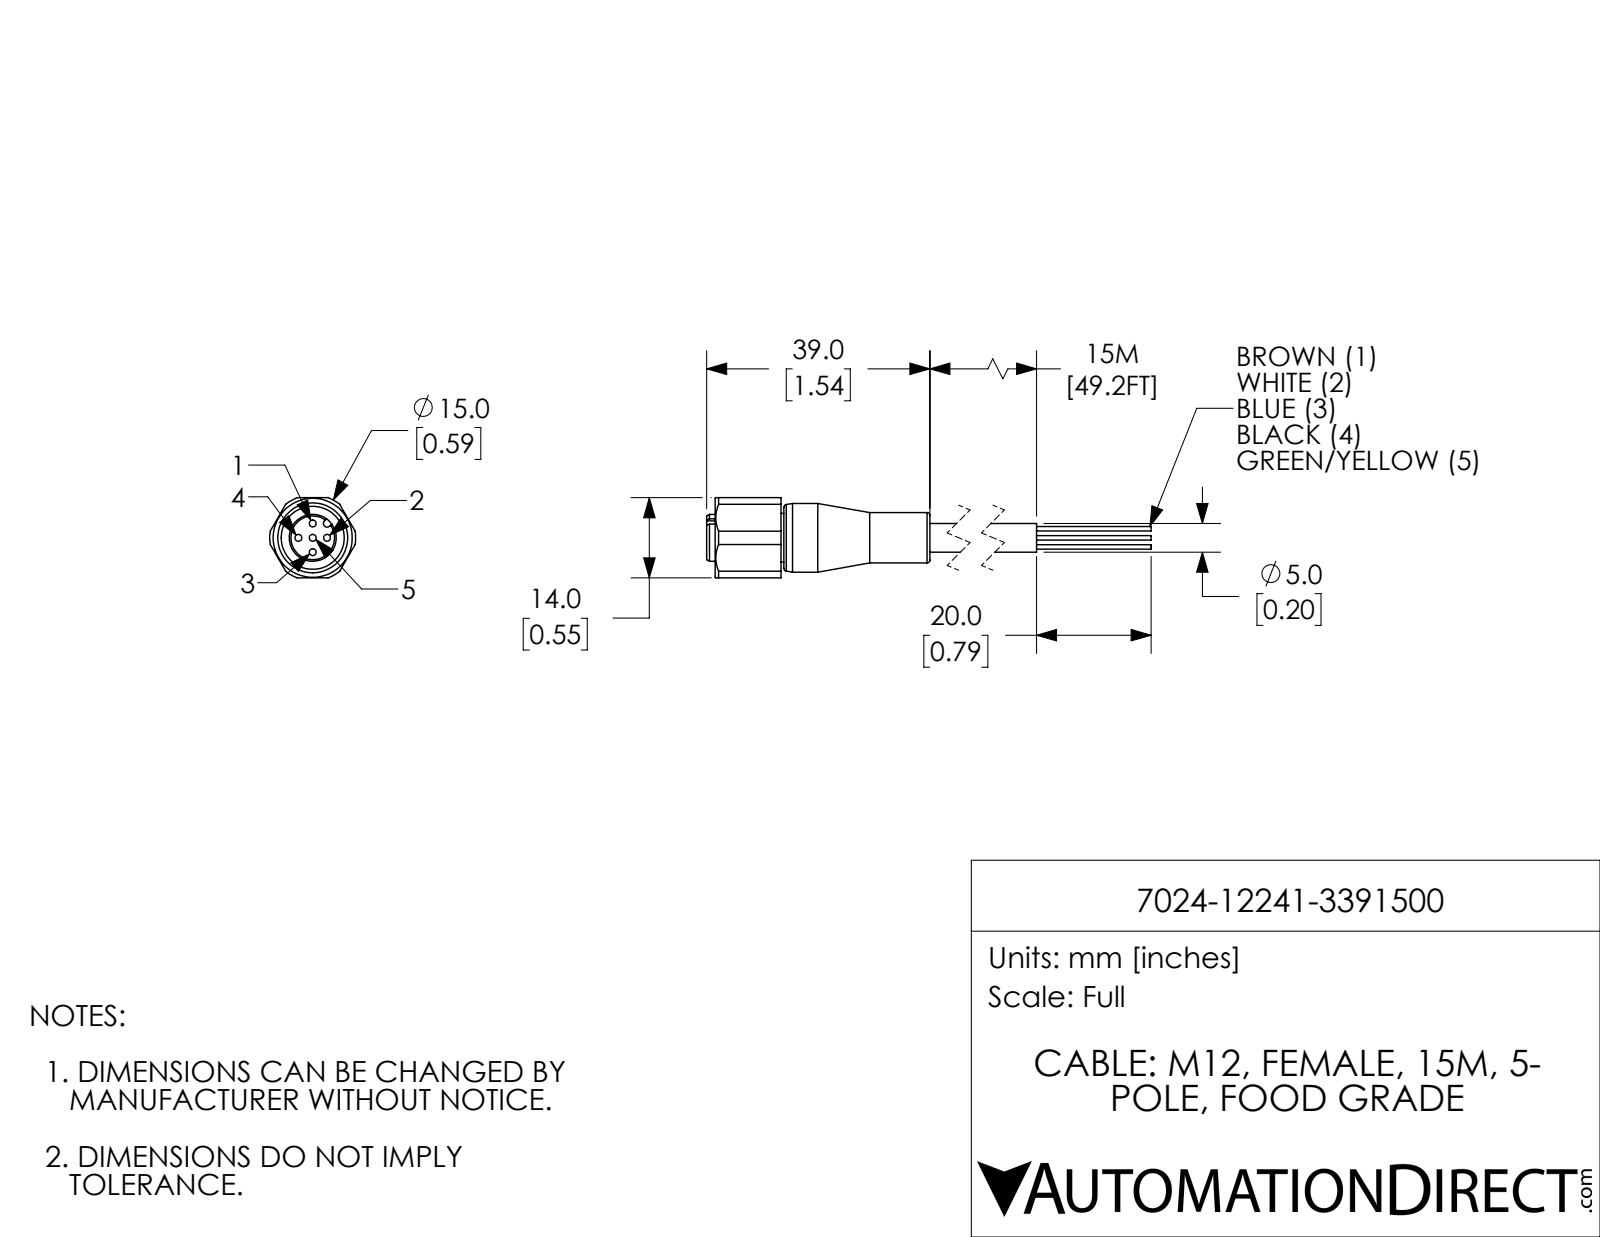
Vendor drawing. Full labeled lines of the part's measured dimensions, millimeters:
Part name (STEP PRODUCT): 7024-12241-3391500
STEP written by: SolidWorks 2018 (AUTOMOTIVE_DESIGN)
Units: millimetres
Bodies: 1 solid, 80 faces (26 planar, 39 cylindrical, 15 other)
Overall size (bounding box): 77.8 × 15 × 14
Volume: 4 125 mm³ · Surface area: 2 876 mm²
Round holes (diameter × count): ⌀1.2 ×5, ⌀11 ×1
Round bosses / shafts (diameter × count): ⌀0.76 ×5, ⌀12 ×1, ⌀8.8 ×1, ⌀8.5 ×1, ⌀8.2 ×1, ⌀5 ×1
Partial cylindrical surfaces — rounded edges, fillets, slot ends (radius × count): R0.65 ×1, R7.5 ×1
Main face-to-face distances: 14, 4, 9, 13, 1.5, 7.5, 11.5, 13.5, 12, 4.5
Hole centre spacings: 2.5, 3.54, 5
